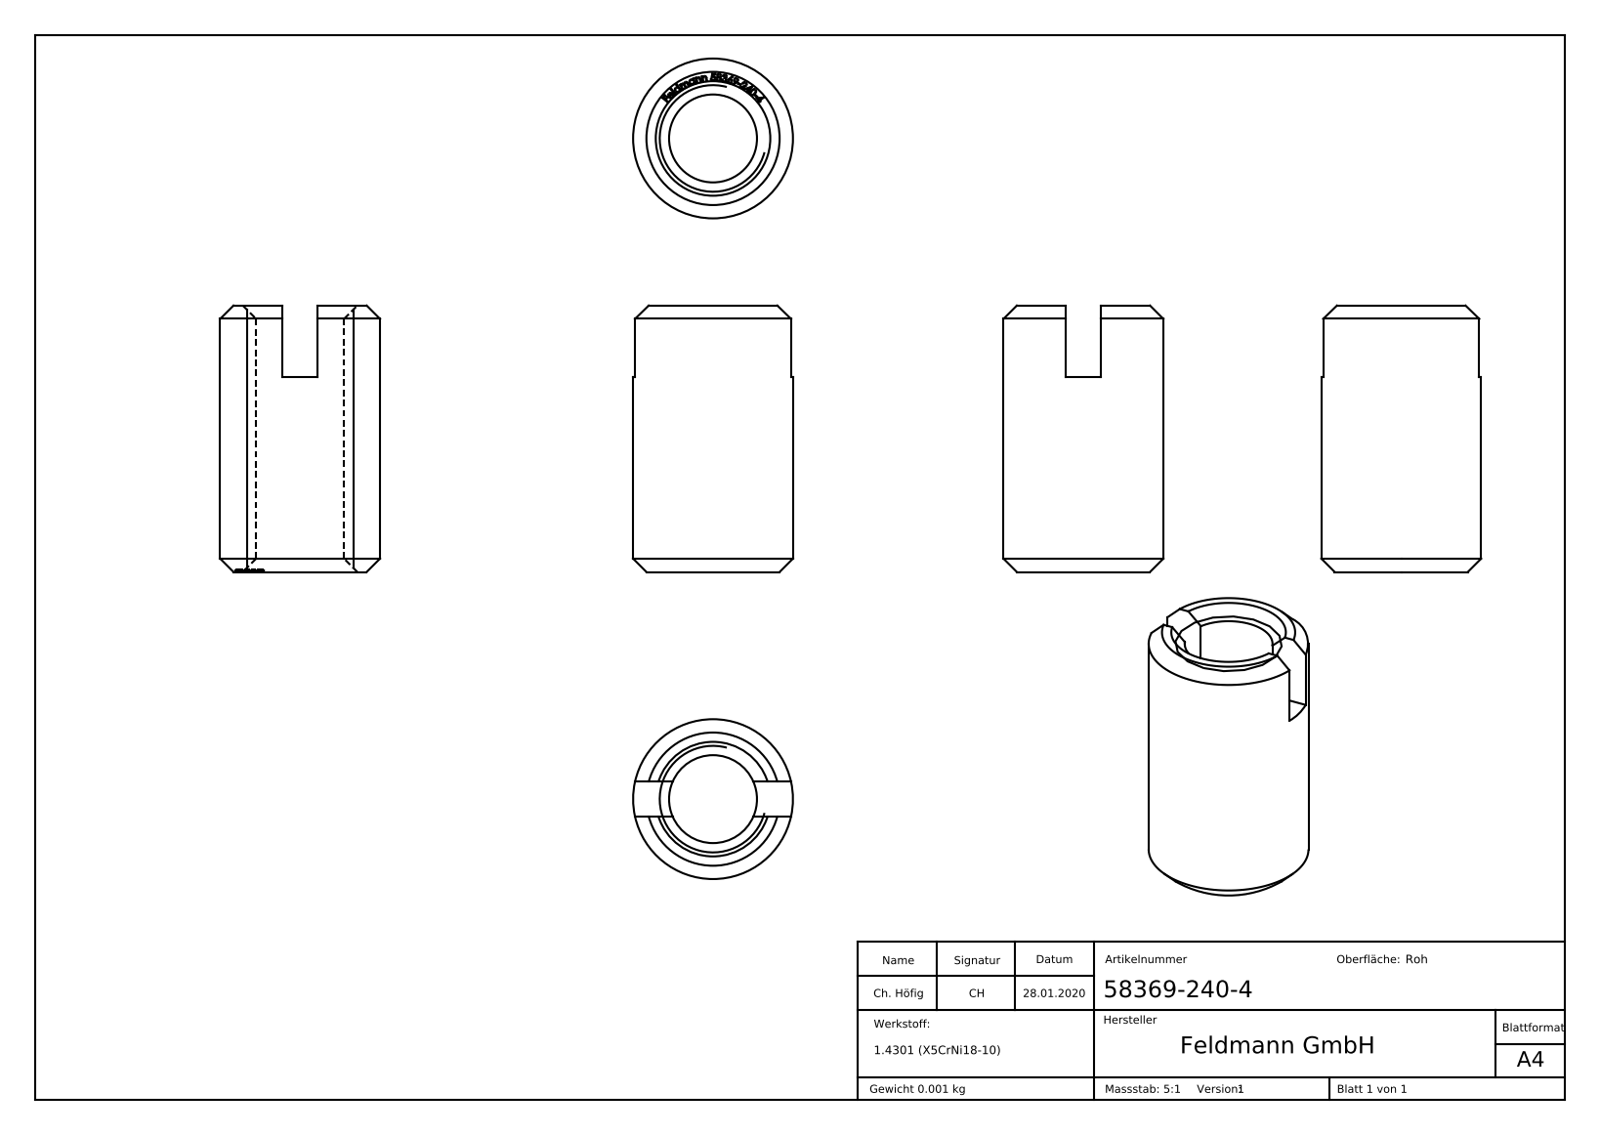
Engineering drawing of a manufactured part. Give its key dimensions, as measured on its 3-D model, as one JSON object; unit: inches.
{"part_name": "58369-240-4", "step_written_by": "SolidWorks 2015 (CONFIG_CONTROL_DESIGN)", "units": "inches", "bodies": {"solids": 1, "faces": 275, "planar": 147, "cylindrical": 2, "other": 126}, "overall_size": [1.024, 0.236, 0.236], "volume_in3": 0.011, "surface_area_in2": 0.493, "round_holes": [[0.13, 1]], "round_bosses_or_shafts": [[0.236, 1]], "face_to_face_distances": [0.051, 0.394, 0.287, 0.106, 0.283, 0.39, 0.086, 0.085, 0.1, 0.089]}
